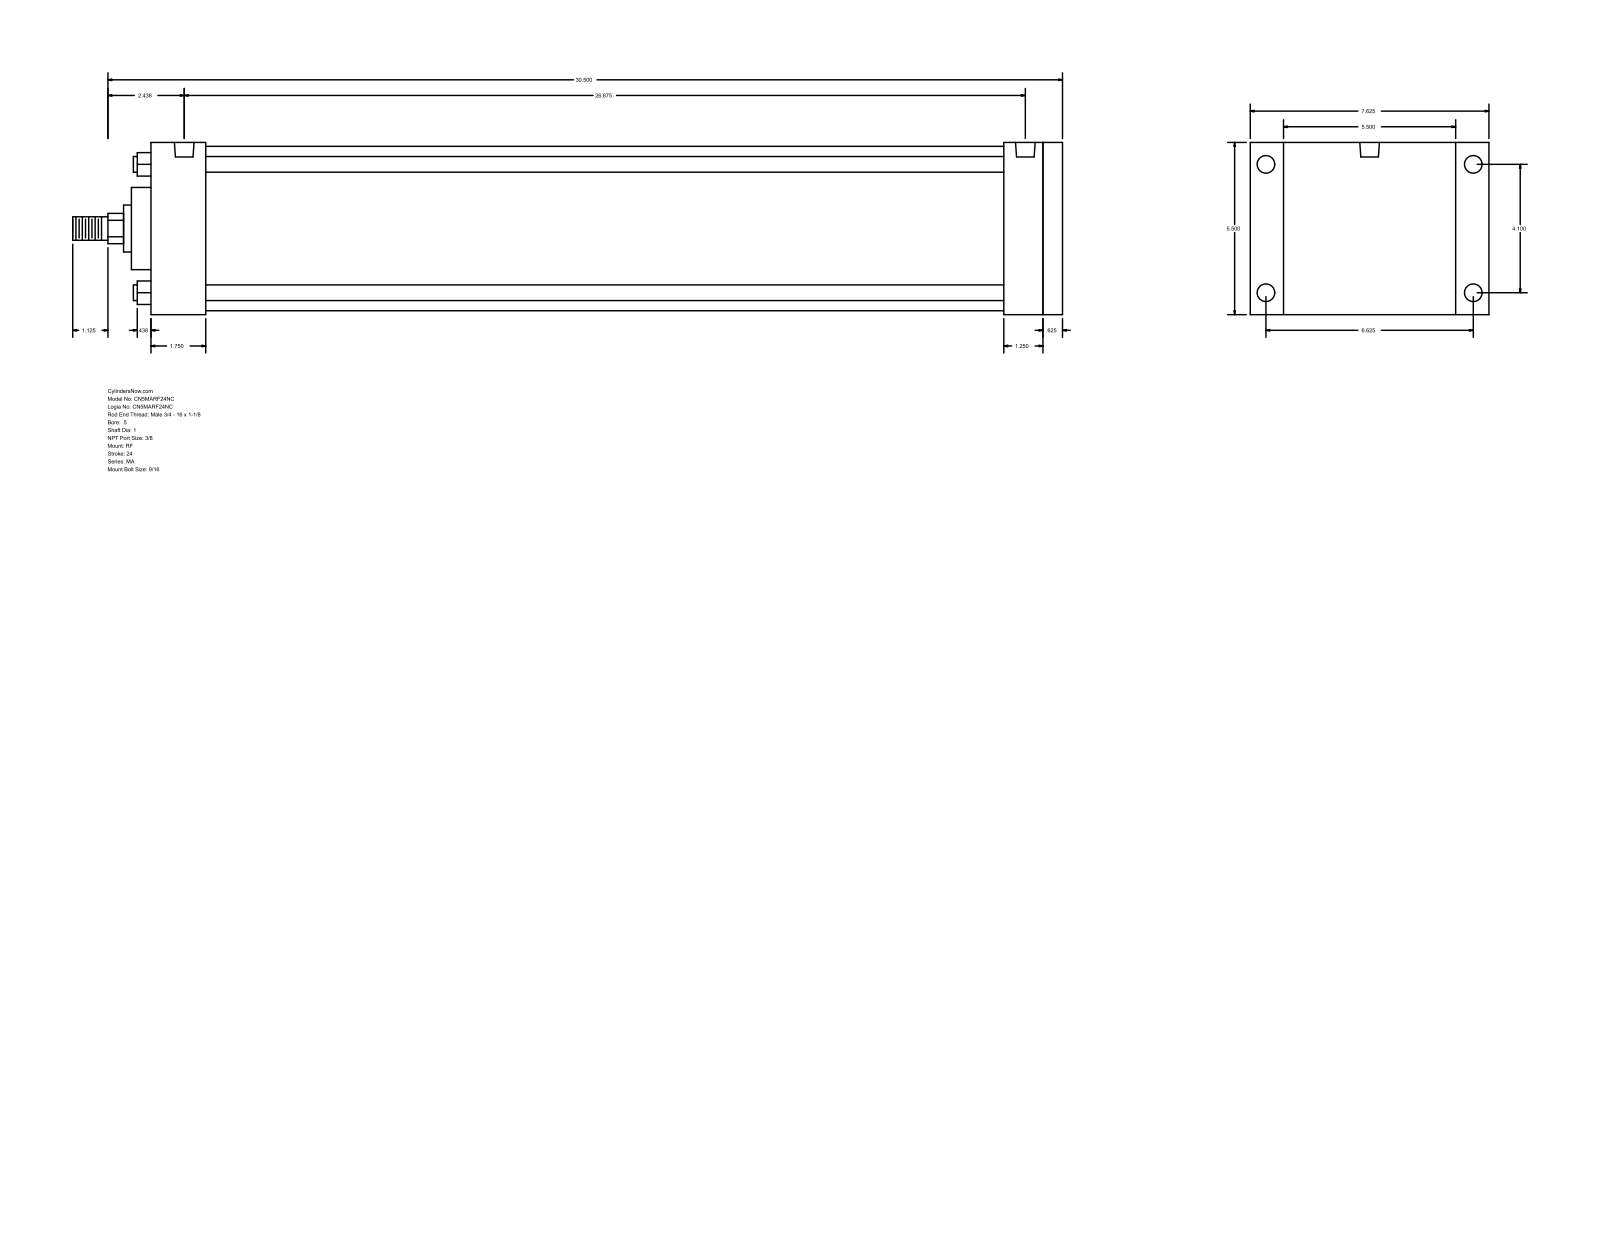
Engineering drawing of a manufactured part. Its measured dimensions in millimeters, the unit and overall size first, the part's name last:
Units: millimetres
Overall size (bounding box): 803.27 × 193.68 × 139.7
Round holes (diameter × count): ⌀11.11 ×4, ⌀14.29 ×4, ⌀15.93 ×2
Round bosses / shafts (diameter × count): ⌀12.7 ×4, ⌀133.35 ×1, ⌀66.67 ×1, ⌀38.1 ×1, ⌀25.4 ×1, ⌀19.05 ×1
Partial cylindrical surfaces — rounded edges, fillets, slot ends (radius × count): R12.29 ×1
Main face-to-face distances: 139.7, 739.78, 15.87, 723.91, 47.62, 44.46, 679.45, 695.32, 692.16, 647.7
Hole centre spacings: 104.14, 168.28, 197.9, 673.1, 4.76, 4.77, 677.86, 677.87
Bodies: 0 solids, 94 faces (65 planar, 29 cylindrical, 0 other)
Part name (STEP PRODUCT): MA_RF__0500_1
STEP written by: GSSL Pune (CONFIG_CONTROL_DESIGN)
